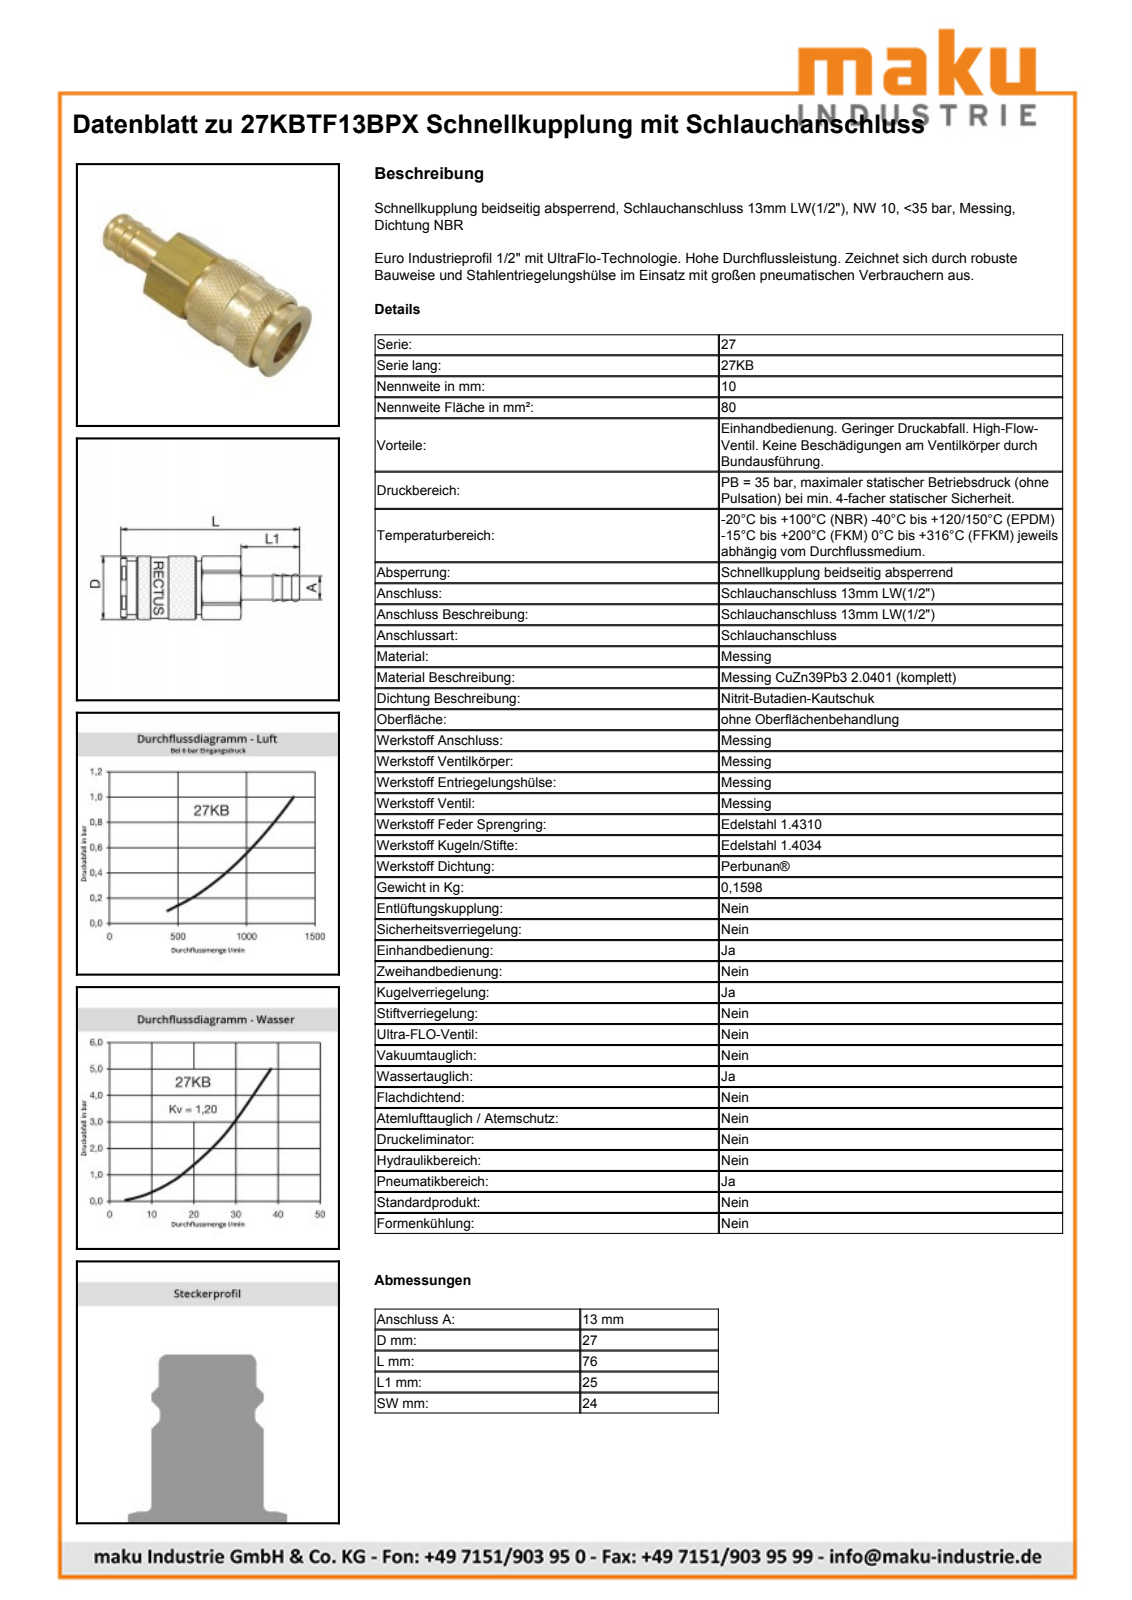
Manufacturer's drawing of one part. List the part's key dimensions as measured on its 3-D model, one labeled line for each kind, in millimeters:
Part name (STEP PRODUCT): D106464
STEP written by: Autodesk Inventor 2011 (AUTOMOTIVE_DESIGN)
Units: millimetres
Bodies: 2 solids, 832 faces (323 planar, 89 cylindrical, 420 other)
Overall size (bounding box): 76.5 × 27.15 × 27.15
Volume: 28 354 mm³ · Surface area: 11 332 mm²
Round holes (diameter × count): ⌀19 ×1, ⌀20.3 ×1, ⌀20.95 ×1, ⌀23.35 ×1, ⌀23.55 ×1
Round bosses / shafts (diameter × count): ⌀27.15 ×1, ⌀26 ×1, ⌀23.1 ×1, ⌀22.75 ×1, ⌀20 ×1, ⌀19 ×1, ⌀13.1 ×1
Partial cylindrical surfaces — rounded edges, fillets, slot ends (radius × count): R8.59 ×1, R12.9 ×1, R13.53 ×1
Main face-to-face distances: 24, 51.5, 25, 24.02, 49, 76.5, 31.75, 19.75, 44.75, 6.25
